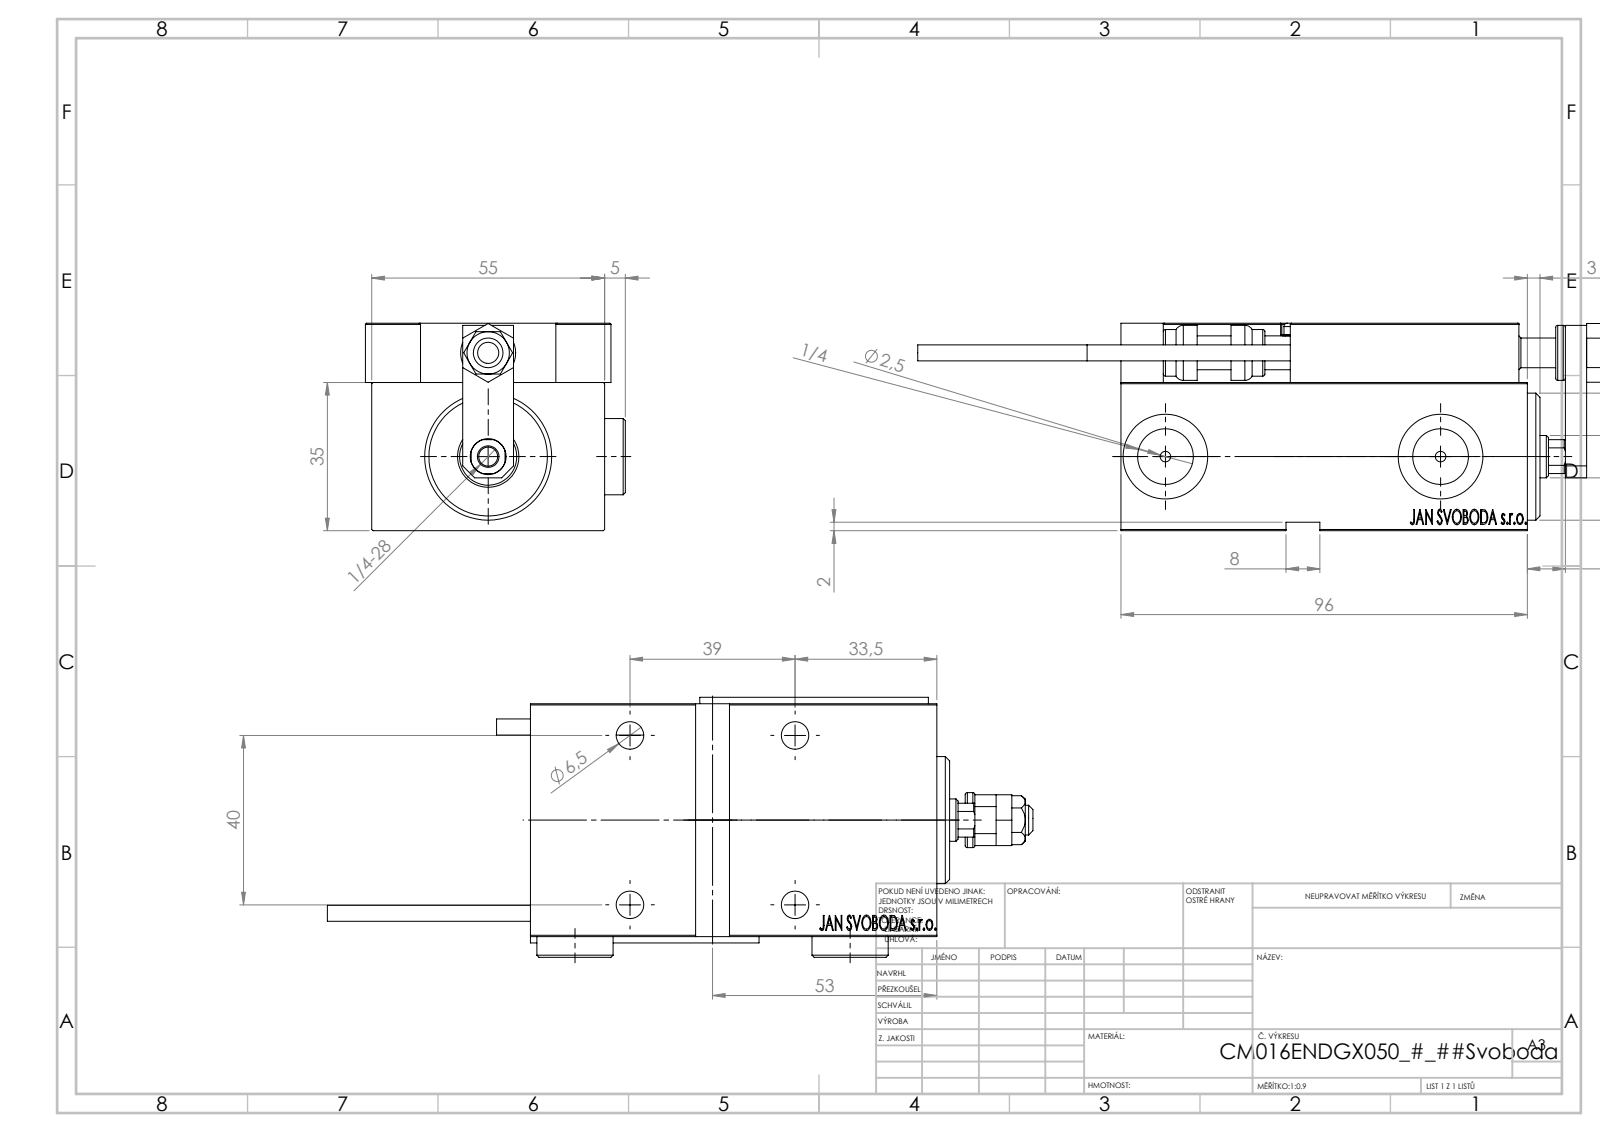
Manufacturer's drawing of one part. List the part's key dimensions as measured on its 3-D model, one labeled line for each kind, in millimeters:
Part name (STEP PRODUCT): V450CM_VC_B; Block; NUT_D10; V450CM_E_VCP (+8 more)
STEP written by: SolidWorks 2019 (CONFIG_CONTROL_DESIGN)
Units: millimetres
Bodies: 26 solids, 1350 faces (605 planar, 200 cylindrical, 545 other)
Overall size (bounding box): 166.7 × 61.4 × 49
Volume: 213 227 mm³ · Surface area: 63 202 mm²
Round holes (diameter × count): ⌀8 ×5, ⌀3.2 ×4, ⌀4 ×4, ⌀6.5 ×4, ⌀10.5 ×4, ⌀2.5 ×2, ⌀5 ×2, ⌀13.16 ×2, ⌀20 ×2, ⌀4.5 ×1, ⌀7 ×1, ⌀8.5 ×1
Round bosses / shafts (diameter × count): ⌀18 ×3, ⌀5 ×2, ⌀3.8 ×2, ⌀30 ×1, ⌀13 ×1, ⌀11 ×1
Partial cylindrical surfaces — rounded edges, fillets, slot ends (radius × count): R0.3 ×30, R3 ×2, R4.5 ×1
Main face-to-face distances: 35, 14, 55, 5, 49, 10, 1.5, 3, 7, 45
Hole centre spacings: 11.37, 20, 21.03, 28.32, 29.59, 29.69, 35.25, 36.06
